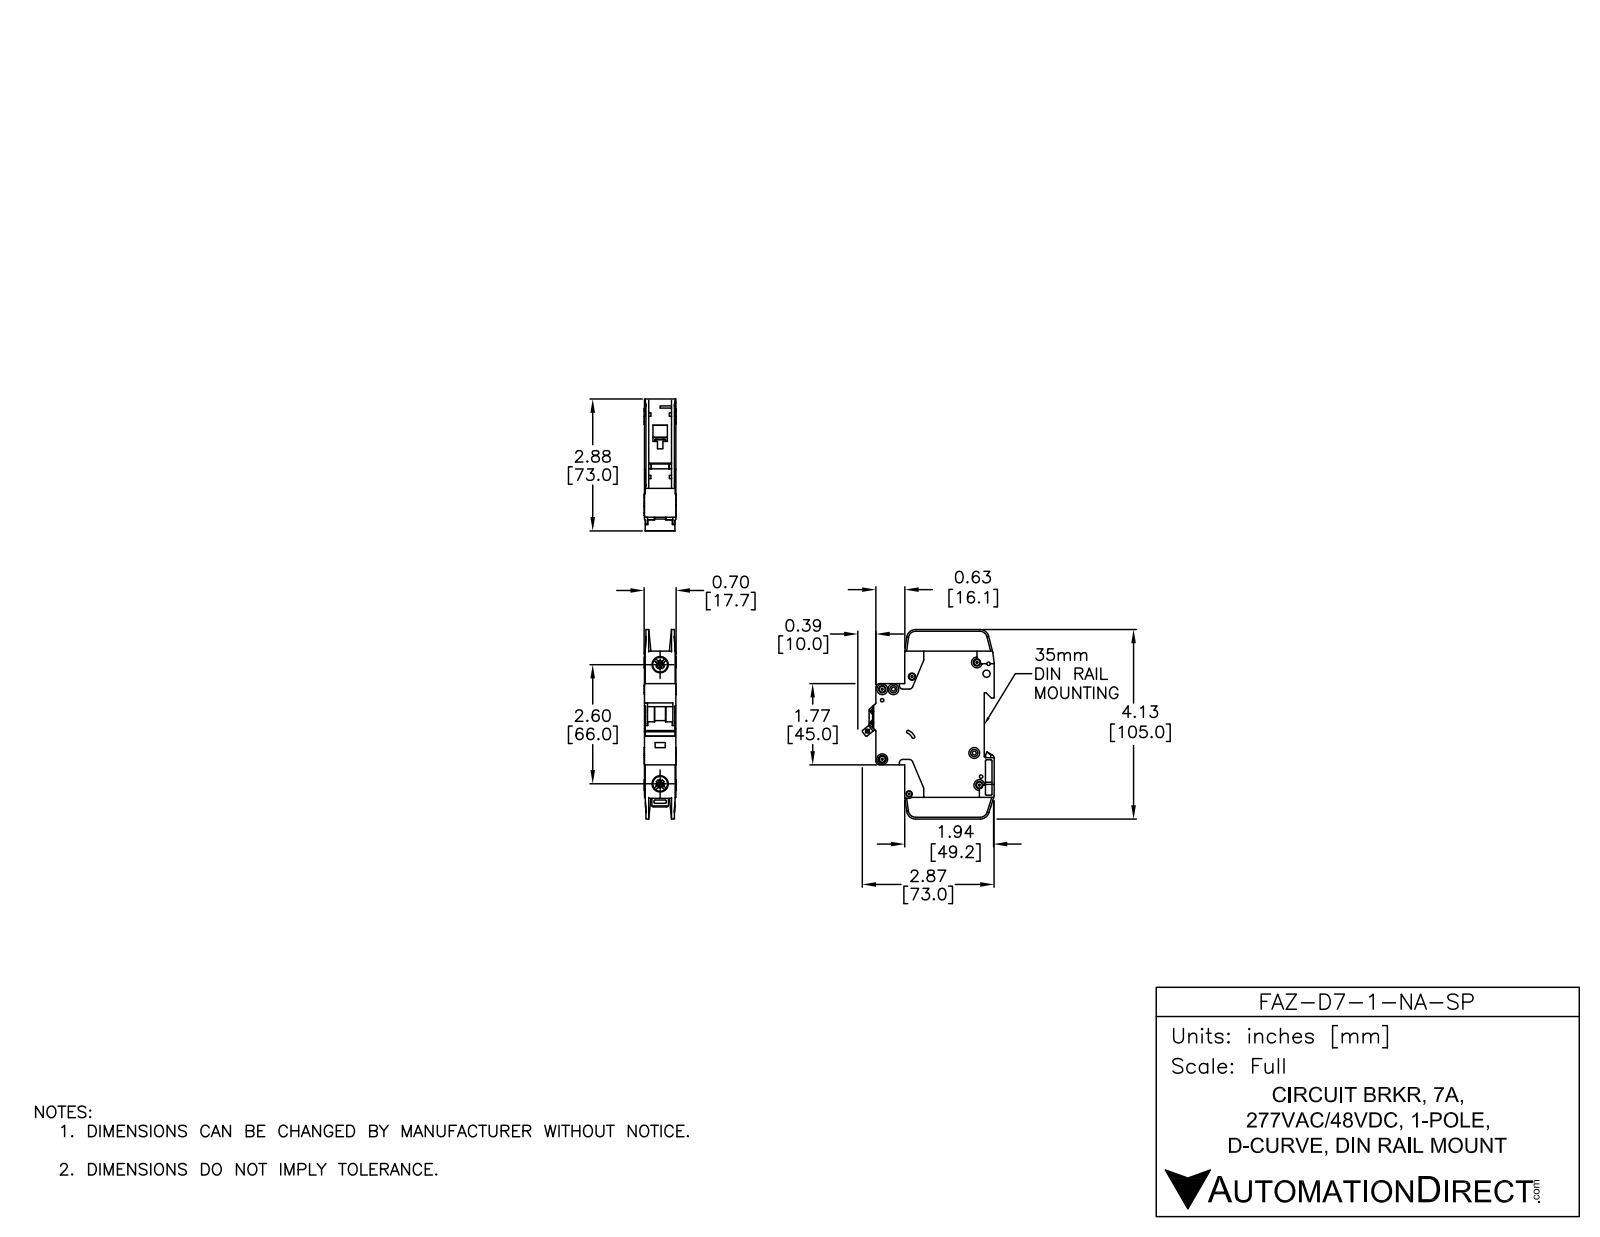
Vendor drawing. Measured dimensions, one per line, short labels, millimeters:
name: FAZ-D7-1-NA-SP
written by: SolidWorks 2014 (AUTOMOTIVE_DESIGN)
unit: mm
bodies: 3 solids, 784 faces (409 planar, 263 cylindrical, 112 other)
size: 105 × 73.04 × 17.7
volume: 77 695 mm³; area: 24 740 mm²
holes: 7× ⌀3.6, 2× ⌀1.09, 2× ⌀1.5, 2× ⌀4, 2× ⌀7.15, 2× ⌀8.2, 1× ⌀1.9, 1× ⌀2.15, 1× ⌀2.2, 1× ⌀2.55, 1× ⌀3.3, 1× ⌀3.4
bosses: 7× ⌀6, 1× ⌀2.5
rounds: 29× R0.25, 18× R0.5, 10× R1, 10× R2, 5× R5, 4× R4, 3× R1.8, 2× R0.2
face distances: 17.5, 15.05, 0.7, 2.45, 1.75, 15.75, 13.3, 14, 12.6, 2
hole spacings: 6.2, 5.19, 6.1, 8.19, 8.56, 8.7, 11.11, 12.45
